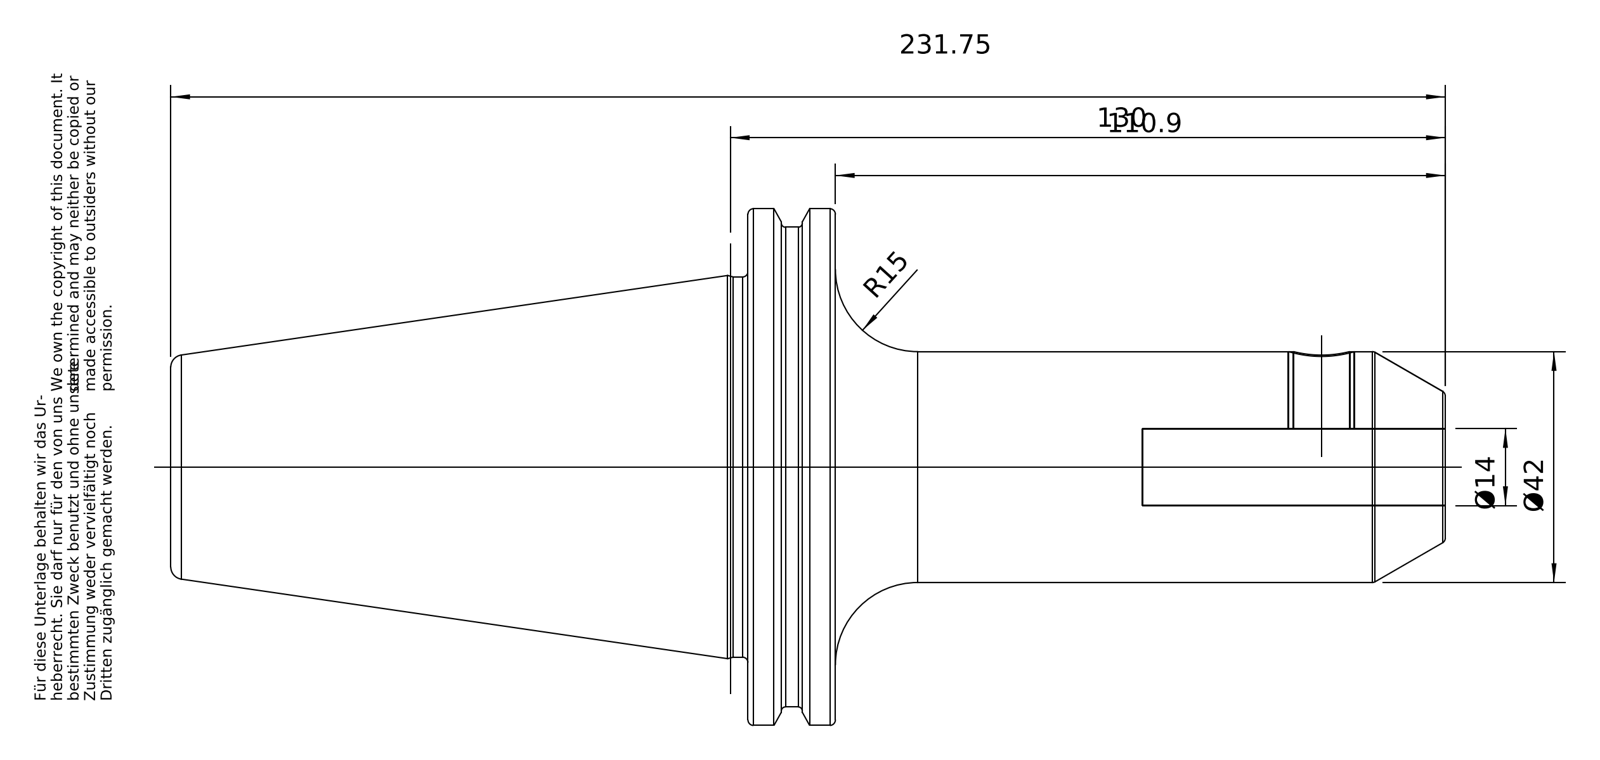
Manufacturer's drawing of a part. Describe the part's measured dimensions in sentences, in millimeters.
The part is named "50-304-14". Its 3-D file was written by "PRO/ENGINEER BY PARAMETRIC TECHNOLOGY CORPORATION, 2010430 (CONFIG_CONTROL_DESIGN)". It is 1 solid with 103 faces: 21 planar, 32 cylindrical and 50 other. Overall it measures 231.6 by 97.47 by 94 millimeters. Its volume is 485 149 cubic millimeters and its surface area 58 872 square millimeters. Round holes: 1 of diameter 10.2, 1 of diameter 12, 1 of diameter 14, 1 of diameter 20.75, 1 of diameter 25.01, 1 of diameter 25.7. Round bosses or shafts: 1 of diameter 91, 1 of diameter 69.15, 1 of diameter 42, 1 of diameter 24.01. Partial cylindrical surfaces (rounded edges, fillets, slot ends): 5 of radius 1.75, 1 of radius 48.74. The main face-to-face distances are 15.85, 104.8, 120.65, 231.6, 126.8, 110.95, 72.8, 25.8, 176.5, 71.7.
